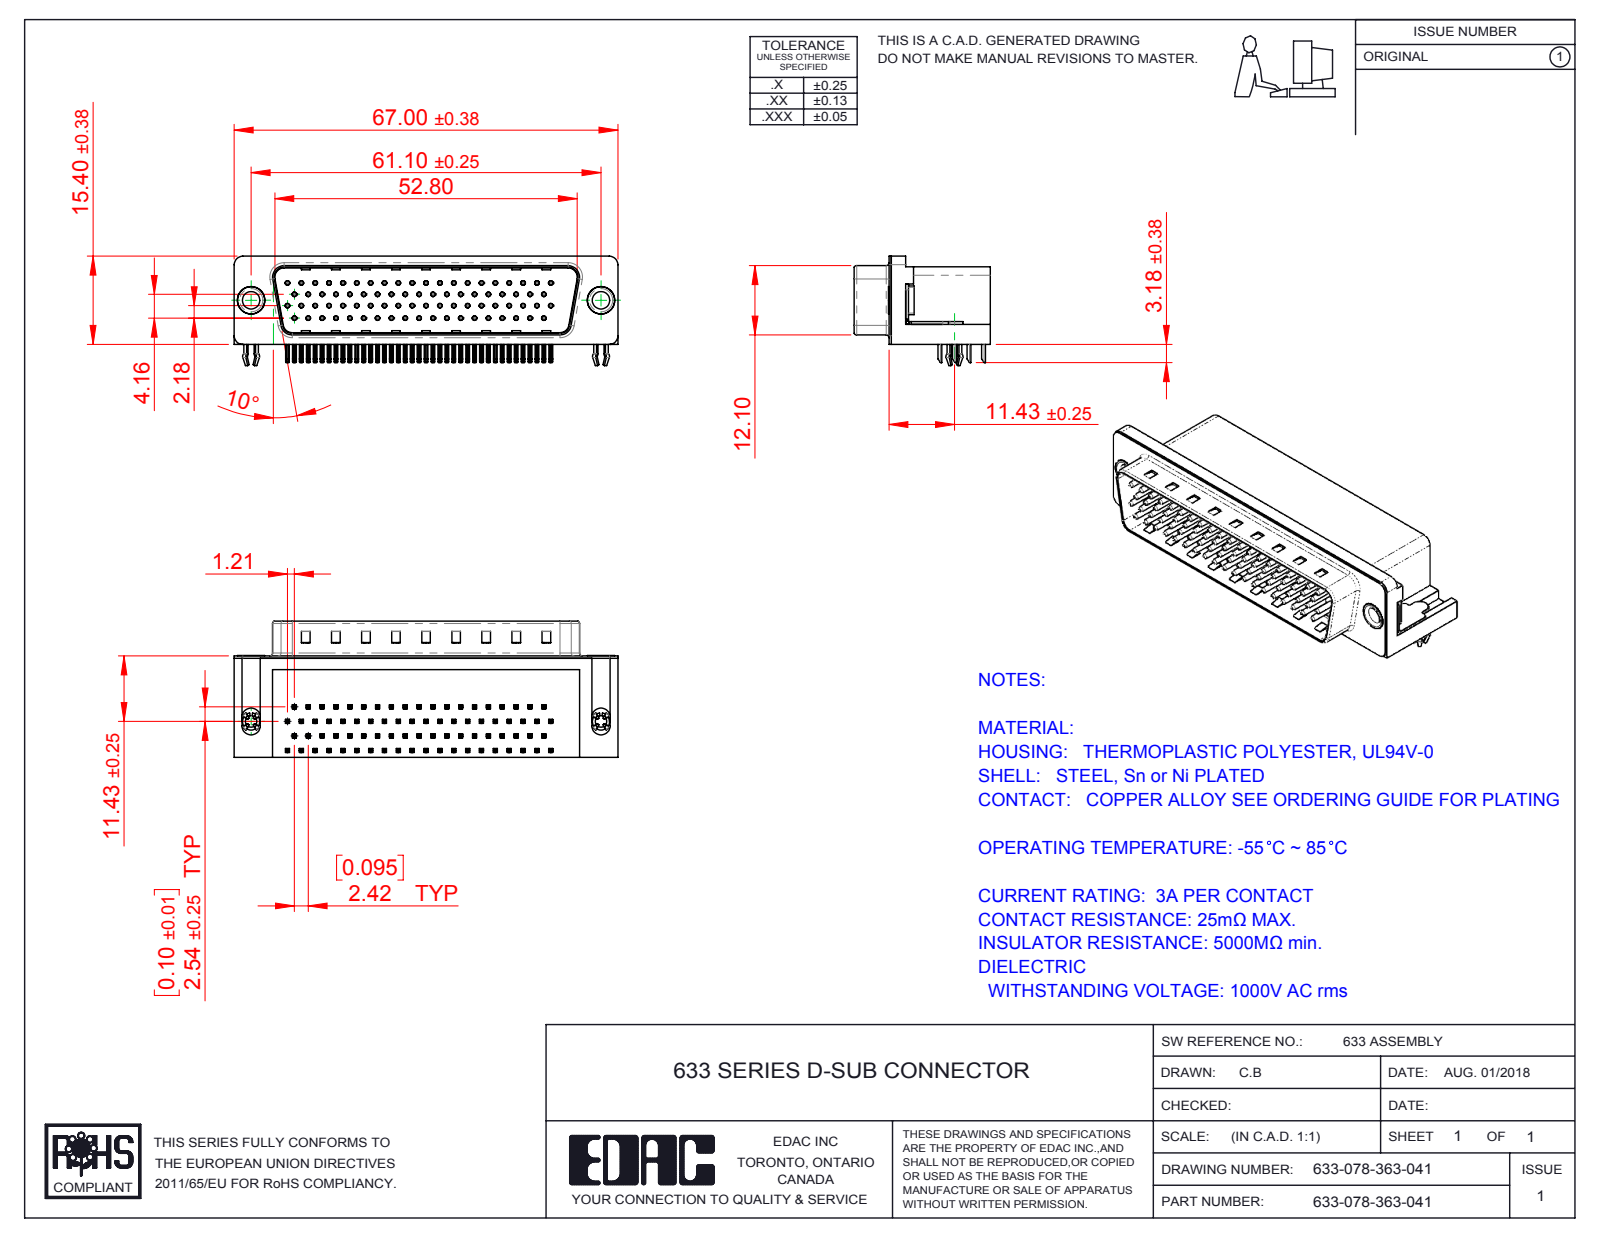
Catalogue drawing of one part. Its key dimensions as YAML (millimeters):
part_name: "633-078-363-041; 633 Thru Hole Rivet; 633 4 Prong Board Lock_78 Contact; 633 Housing_78 Contact (+5 more)"
step_written_by: "SolidWorks 2016 (CONFIG_CONTROL_DESIGN)"
units: millimeters
bodies: {solids: 84, faces: 6356, planar: 4023, cylindrical: 1766, other: 567}
overall_size: [67, 23.8, 19.1]
volume: 14611
surface_area: 16410
round_holes:
  - {diameter: 0.35, count: 78}
  - {diameter: 0.8, count: 78}
  - {diameter: 2, count: 2}
  - {diameter: 3.05, count: 2}
  - {diameter: 4, count: 2}
  - {diameter: 4.8, count: 2}
  - {diameter: 5, count: 2}
round_bosses_or_shafts:
  - {diameter: 0.75, count: 78}
  - {diameter: 4.9, count: 2}
  - {diameter: 4.75, count: 2}
  - {diameter: 3.85, count: 2}
  - {diameter: 3, count: 2}
partial_cylinders:
  - {radius: 0.25, count: 324}
  - {radius: 0.12, count: 156}
  - {radius: 1, count: 16}
  - {radius: 0.5, count: 9}
  - {radius: 1.6, count: 8}
  - {radius: 1.5, count: 6}
  - {radius: 0.45, count: 4}
  - {radius: 0.9, count: 4}
face_to_face_distances: [0.4, 13.2, 17.3, 11.7, 13.35, 2.05, 13.75, 1.65, 1.85, 11.9]
hole_center_spacings: [2.42, 4.84, 7.26, 9.68, 6.26, 7.13, 12.1, 8.62]
